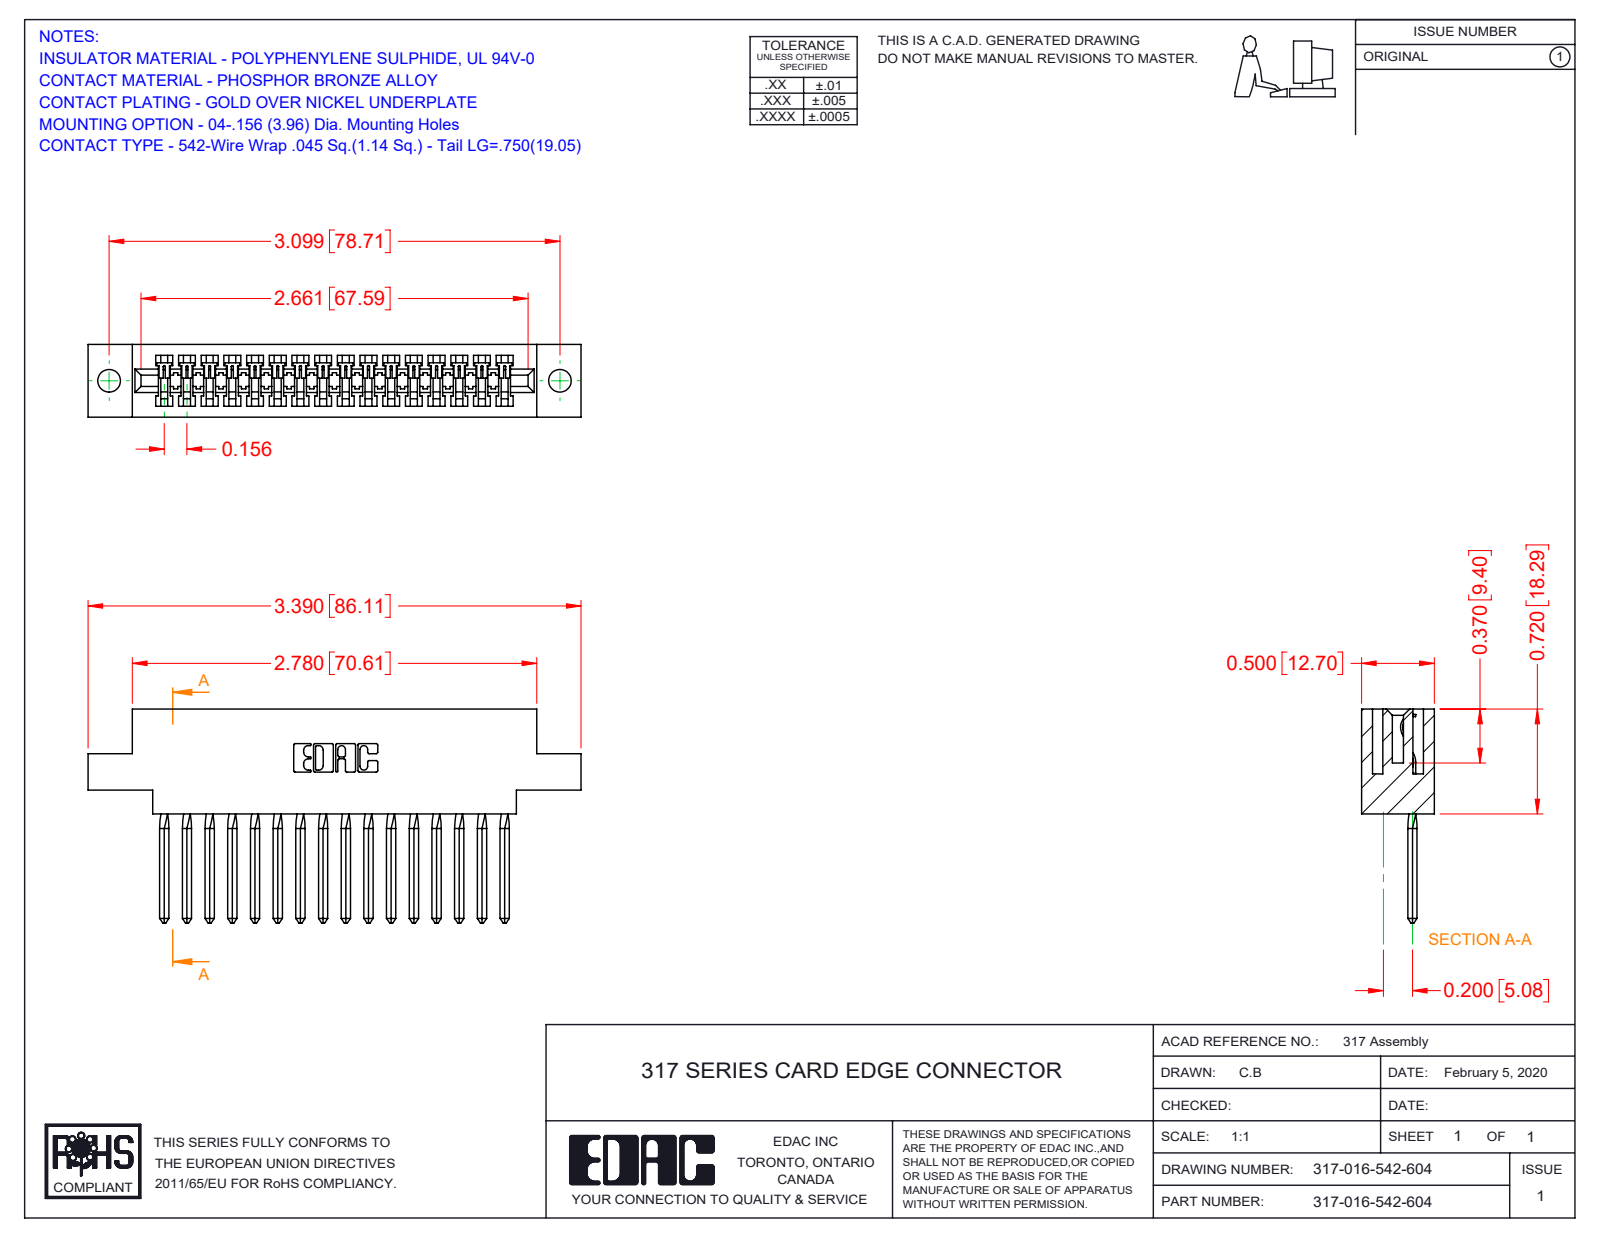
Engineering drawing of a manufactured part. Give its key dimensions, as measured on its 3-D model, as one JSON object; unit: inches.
{"part_name": "317 Part_.156 Dia - TH; 317-290-003_542; 317-016-542-604", "step_written_by": "SolidWorks 2016 (CONFIG_CONTROL_DESIGN)", "units": "inches", "bodies": {"solids": 17, "faces": 1302, "planar": 1082, "cylindrical": 156, "other": 64}, "overall_size": [3.39, 1.47, 0.5], "volume_in3": 0.764, "surface_area_in2": 22.47, "round_holes": [[0.156, 2]], "partial_cylinders_radius": [[0.006, 32], [0.01, 22], [0.007, 6], [0.031, 6], [0.026, 3], [0.074, 1], [0.089, 1], [0.1, 1]], "face_to_face_distances": [0.5, 0.075, 0.425, 0.11, 0.35, 0.065, 0.22, 0.136, 0.72, 0.211], "hole_center_spacings": [3.099]}
